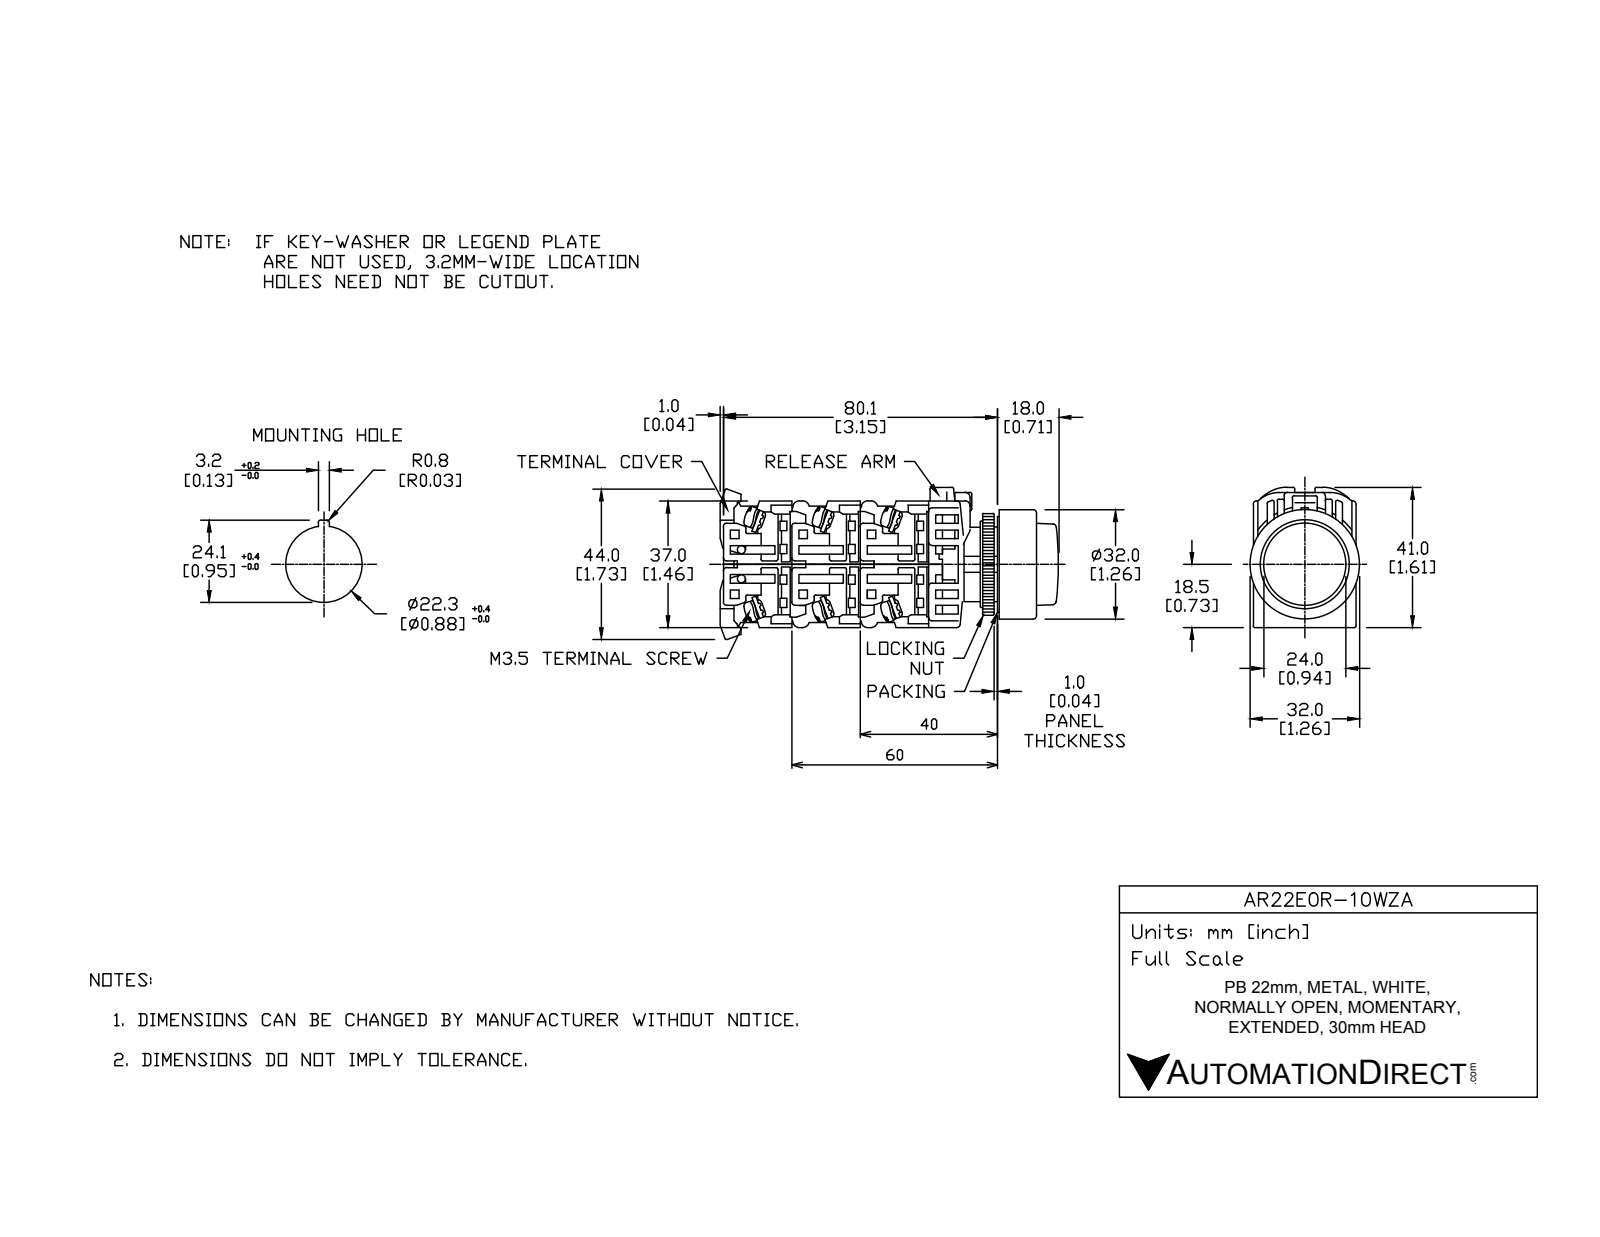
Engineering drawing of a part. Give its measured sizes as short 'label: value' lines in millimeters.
name: AR22E0R-10WZA
written by: SolidWorks 2017 (AUTOMOTIVE_DESIGN)
unit: mm
bodies: 12 solids, 297 faces (201 planar, 74 cylindrical, 22 other)
size: 59.75 × 41 × 32
volume: 30 443 mm³; area: 19 885 mm²
holes: 1× ⌀21.8, 1× ⌀22, 1× ⌀25, 1× ⌀31
bosses: 2× ⌀5, 1× ⌀32, 1× ⌀30.5, 1× ⌀29.8, 1× ⌀24, 1× ⌀23.8, 1× ⌀21.75, 1× ⌀17
rounds: 23× R0.5, 4× R1.75, 4× R5, 2× R4, 1× R16.59, 1× R17.59
face distances: 1, 28.5, 18, 3, 2, 29, 30, 10.5, 8, 20.5
